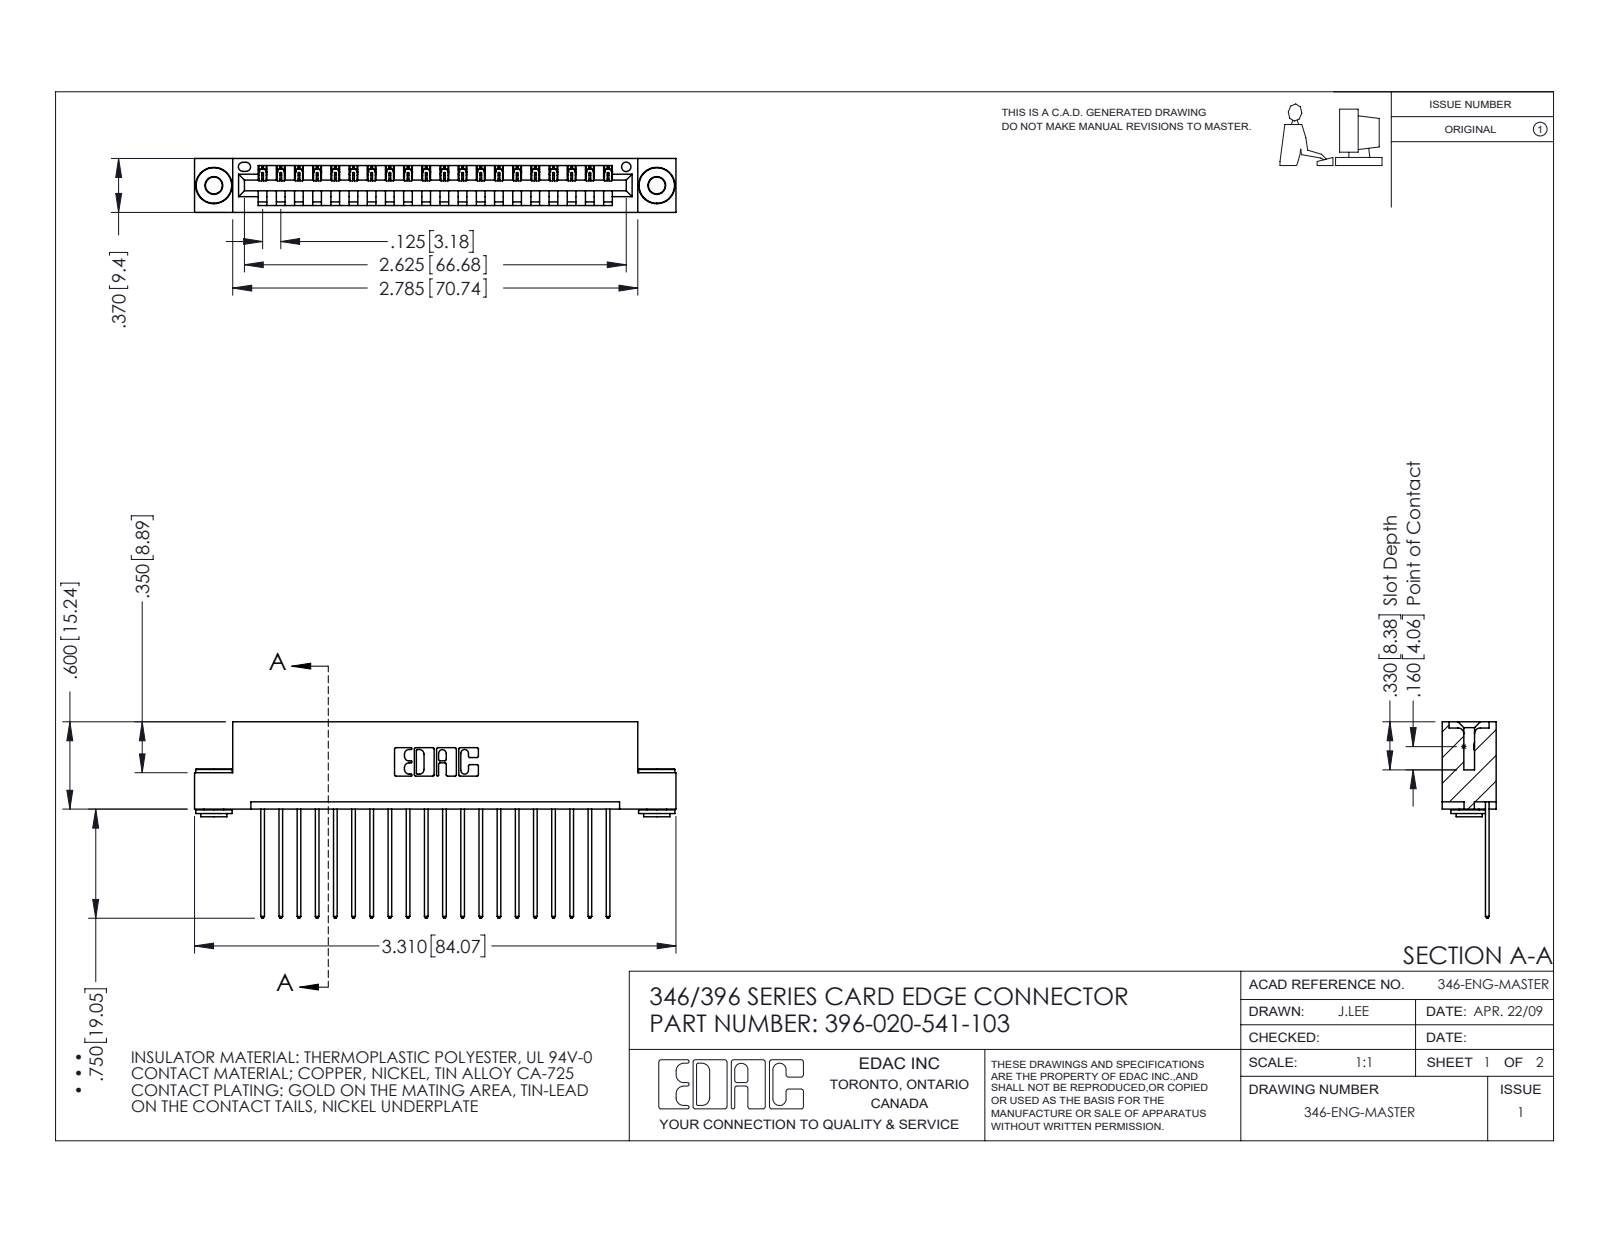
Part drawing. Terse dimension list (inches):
name: 345-292-001_345-293-141; 345-250-002_345-250-002-102; 346 Part_Flush Mounting Lugs - 0.156 Dia-TH; 396-020-541-103
written by: SolidWorks 2016 (CONFIG_CONTROL_DESIGN)
unit: in
bodies: 23 solids, 1320 faces (886 planar, 426 cylindrical, 8 other)
size: 3.31 × 1.35 × 0.37
volume: 0.487 in³; area: 16.05 in²
holes: 2× ⌀0.116, 2× ⌀0.156, 1× ⌀0.064
bosses: 2× ⌀0.25, 2× ⌀0.18, 2× ⌀0.136
rounds: 40× R0.006, 40× R0.01, 22× R0.01, 6× R0.007, 6× R0.031, 3× R0.026, 2× R0.031, 2× R0.04
face distances: 0.048, 0.322, 0.25, 0.37, 0.025, 0.072, 0.298, 0.148, 0.222, 0.1
hole spacings: 0.246, 2.837, 3.045
